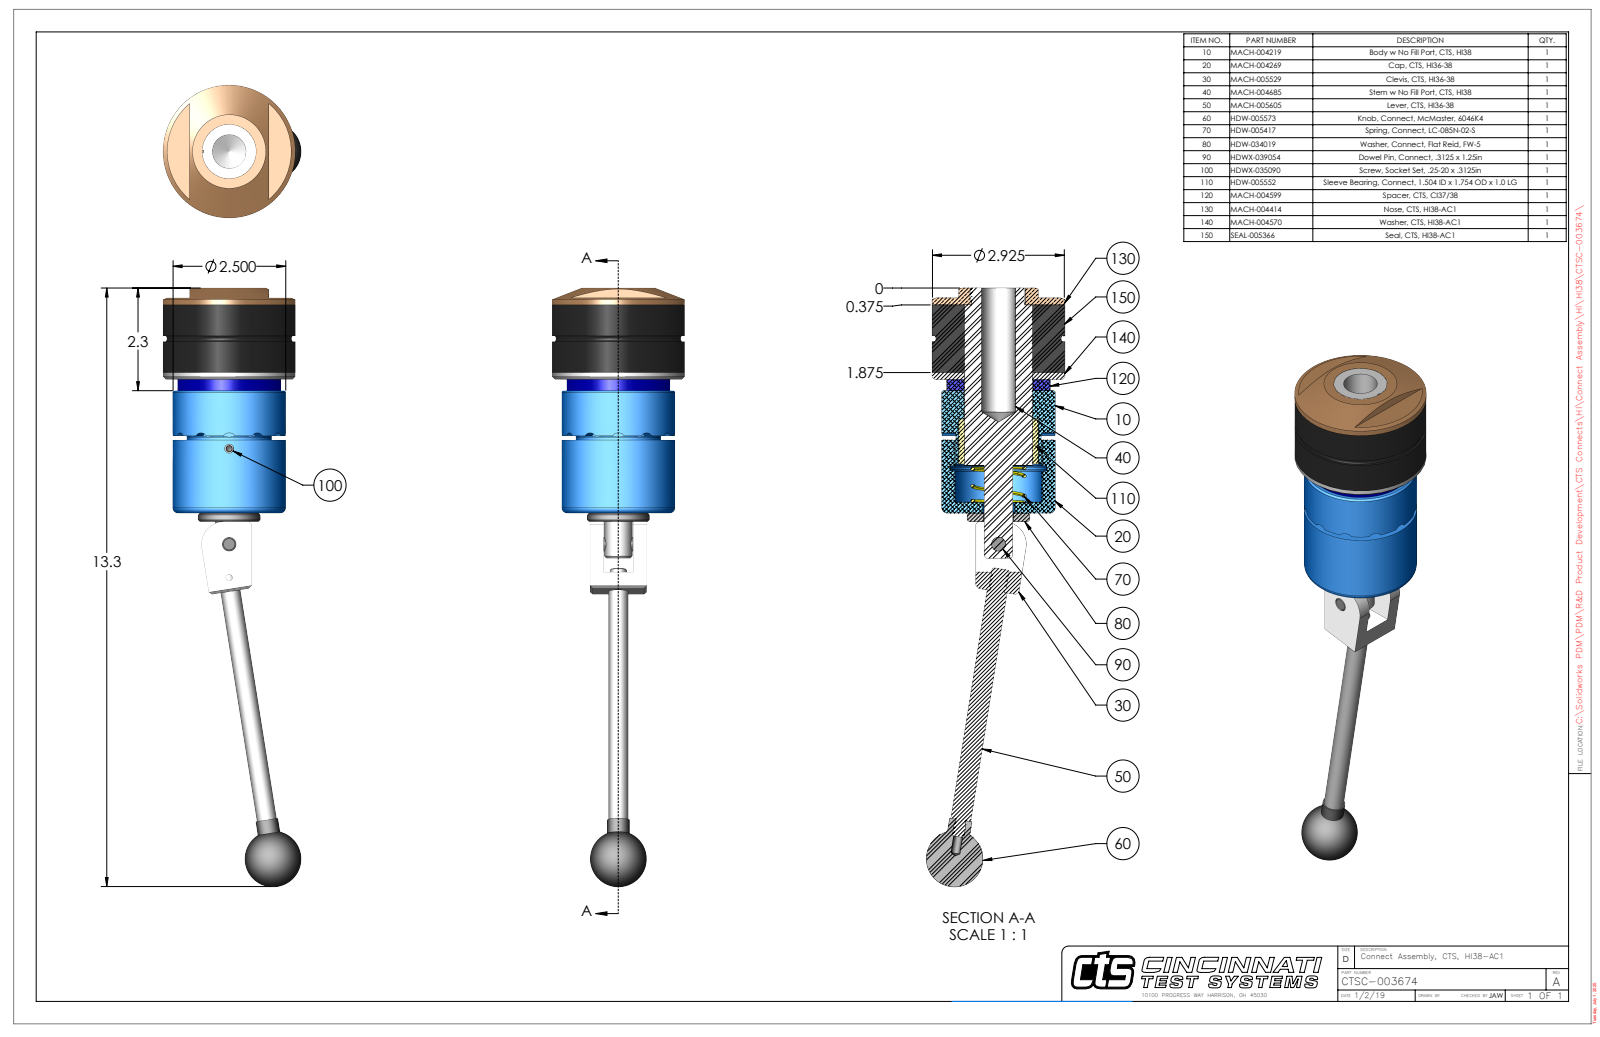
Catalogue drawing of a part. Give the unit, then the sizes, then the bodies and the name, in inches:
Units: inches
Overall size (bounding box): 13.275 × 3.055 × 2.925
Round holes (diameter × count): ⌀0.201 ×2, ⌀0.15 ×1, ⌀0.311 ×1, ⌀0.313 ×1, ⌀0.314 ×1, ⌀0.656 ×1, ⌀0.696 ×1, ⌀0.75 ×1, ⌀1.172 ×1, ⌀1.495 ×1, ⌀1.501 ×1, ⌀1.51 ×1
Round bosses / shafts (diameter × count): ⌀2.925 ×1, ⌀2.925 ×1, ⌀2.5 ×1, ⌀2.281 ×1, ⌀1.875 ×1, ⌀1.5 ×1, ⌀1.496 ×1, ⌀1.38 ×1
Partial cylindrical surfaces — rounded edges, fillets, slot ends (radius × count): R0.12 ×12, R0.029 ×2, R0.5 ×1, R1.197 ×1
Main face-to-face distances: 1.5, 0.152, 1.652, 0.25, 0.402, 1.902, 2.713, 2.963, 3.115, 4.615
Hole centre spacings: 0.74, 2.118, 2.858
Volume: 29.19 in³ · Surface area: 152 in²
Bodies: 10 solids, 275 faces (98 planar, 108 cylindrical, 69 other)
Part name (STEP PRODUCT): CTSC-003674
STEP written by: SolidWorks 2023 (AUTOMOTIVE_DESIGN)
